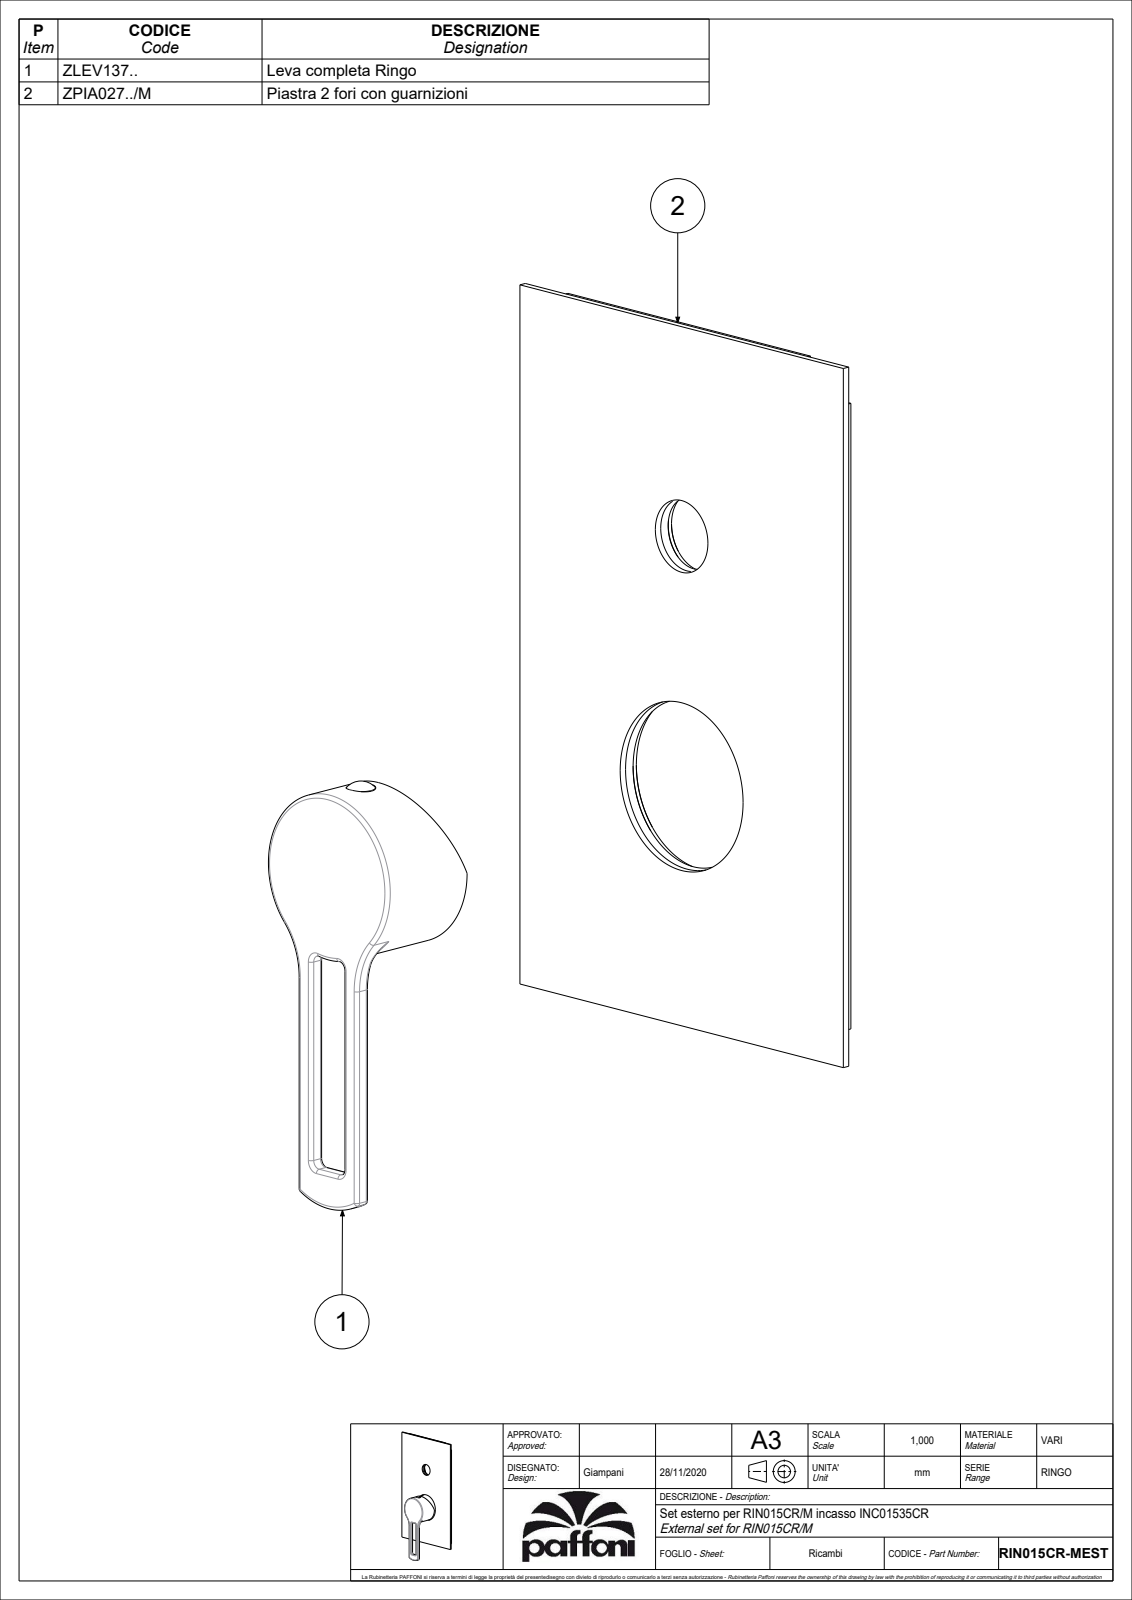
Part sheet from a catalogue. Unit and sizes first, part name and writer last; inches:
Units: inches
Overall size (bounding box): 8.465 × 4.724 × 1.535
Round holes (diameter × count): ⌀0.118 ×1, ⌀0.307 ×1, ⌀0.768 ×1, ⌀0.846 ×1, ⌀0.984 ×1, ⌀1.795 ×1, ⌀1.874 ×1, ⌀2.012 ×1
Round bosses / shafts (diameter × count): ⌀2.15 ×1, ⌀1.764 ×1, ⌀1.122 ×1, ⌀0.299 ×1, ⌀0.217 ×1, ⌀0.197 ×1
Partial cylindrical surfaces — rounded edges, fillets, slot ends (radius × count): R0.039 ×12, R0.02 ×8, R0.079 ×4, R0.787 ×2, R0.853 ×1
Main face-to-face distances: 0.079, 0.031, 0.11, 1.35, 1.319, 1.24, 1.535, 0.295, 0.217, 0.185
Hole centre spacings: 2.677
Volume: 4.128 in³ · Surface area: 97.03 in²
Bodies: 2 solids, 264 faces (80 planar, 81 cylindrical, 103 other)
Part name (STEP PRODUCT): RIN015CR-MEST
STEP written by: CREO PARAMETRIC BY PTC INC, 2020044 (CONFIG_CONTROL_DESIGN)
